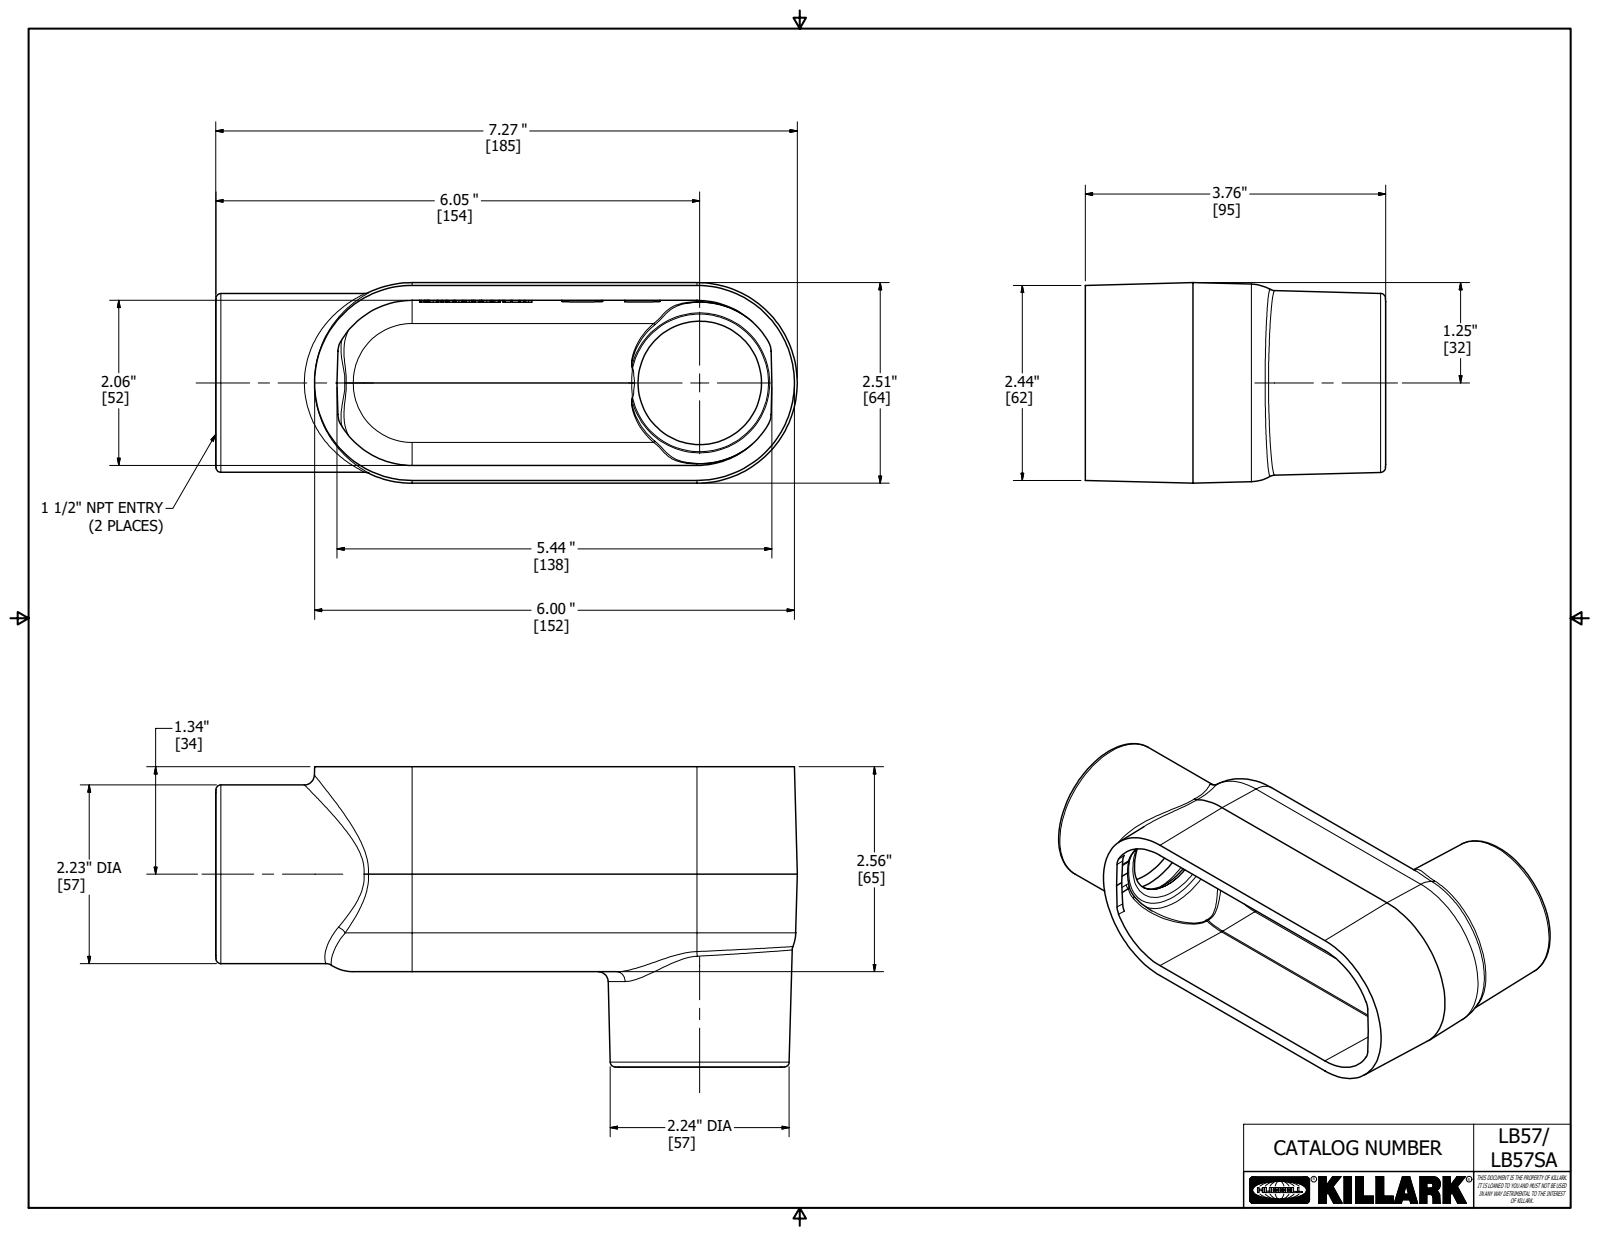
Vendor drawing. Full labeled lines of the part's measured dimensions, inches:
Part name (STEP PRODUCT): 17695-2
STEP written by: Autodesk Inventor 2018 (AUTOMOTIVE_DESIGN)
Units: inches
Bodies: 1 solid, 875 faces (511 planar, 33 cylindrical, 331 other)
Overall size (bounding box): 7.271 × 3.755 × 2.508
Volume: 11.42 in³ · Surface area: 121.4 in²
Round holes (diameter × count): ⌀1.906 ×2, ⌀0.047 ×1, ⌀0.407 ×1, ⌀2.031 ×1
Round bosses / shafts (diameter × count): ⌀2.234 ×1, ⌀0.5 ×1, ⌀0.056 ×1
Partial cylindrical surfaces — rounded edges, fillets, slot ends (radius × count): R0.125 ×4, R0.5 ×4, R0.313 ×2, R0.006 ×1, R0.009 ×1, R0.016 ×1, R0.062 ×1, R0.063 ×1
Main face-to-face distances: 0.188, 2.32, 2.508, 2.132, 2.563, 0.031, 2.531, 2.289, 2.101, 0.031
Hole centre spacings: 0.122
